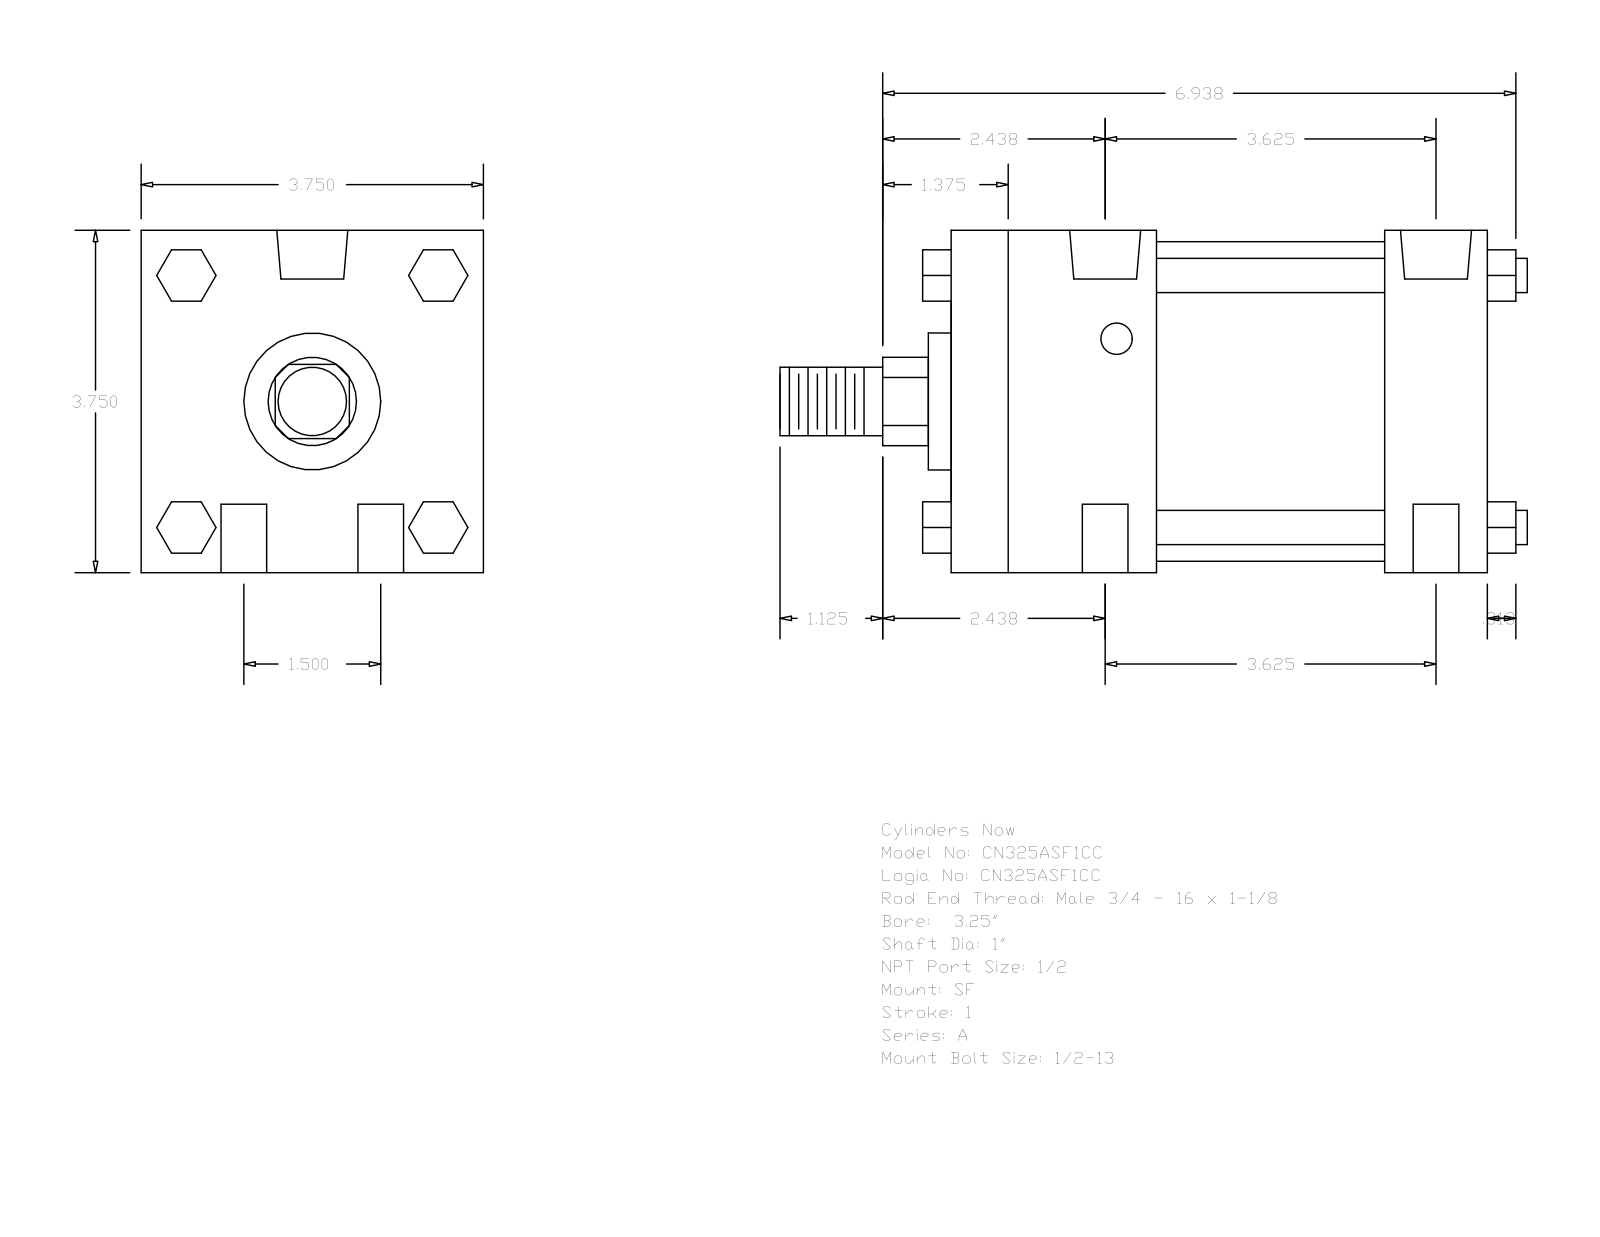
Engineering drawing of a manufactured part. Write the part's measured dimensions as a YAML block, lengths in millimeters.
part_name: "A_SF__0325_1"
step_written_by: "GSSL Pune (CONFIG_CONTROL_DESIGN)"
units: millimeters
bodies: {solids: 0, faces: 124, planar: 94, cylindrical: 30, other: 0}
overall_size: [207.96, 95.25, 95.25]
round_holes:
  - {diameter: 12.7, count: 4}
  - {diameter: 8.73, count: 2}
  - {diameter: 19.77, count: 2}
round_bosses_or_shafts:
  - {diameter: 9.53, count: 4}
  - {diameter: 88.9, count: 1}
  - {diameter: 38.1, count: 1}
  - {diameter: 25.4, count: 1}
  - {diameter: 19.05, count: 1}
partial_cylinders:
  - {radius: 12.29, count: 1}
face_to_face_distances: [95.24, 149.23, 63.5, 120.65, 28.58, 57.15, 92.08, 14.28, 35.05, 60.71]
hole_center_spacings: [19.05, 94.03, 92.08, 38.1, 99.65, 85.72]
